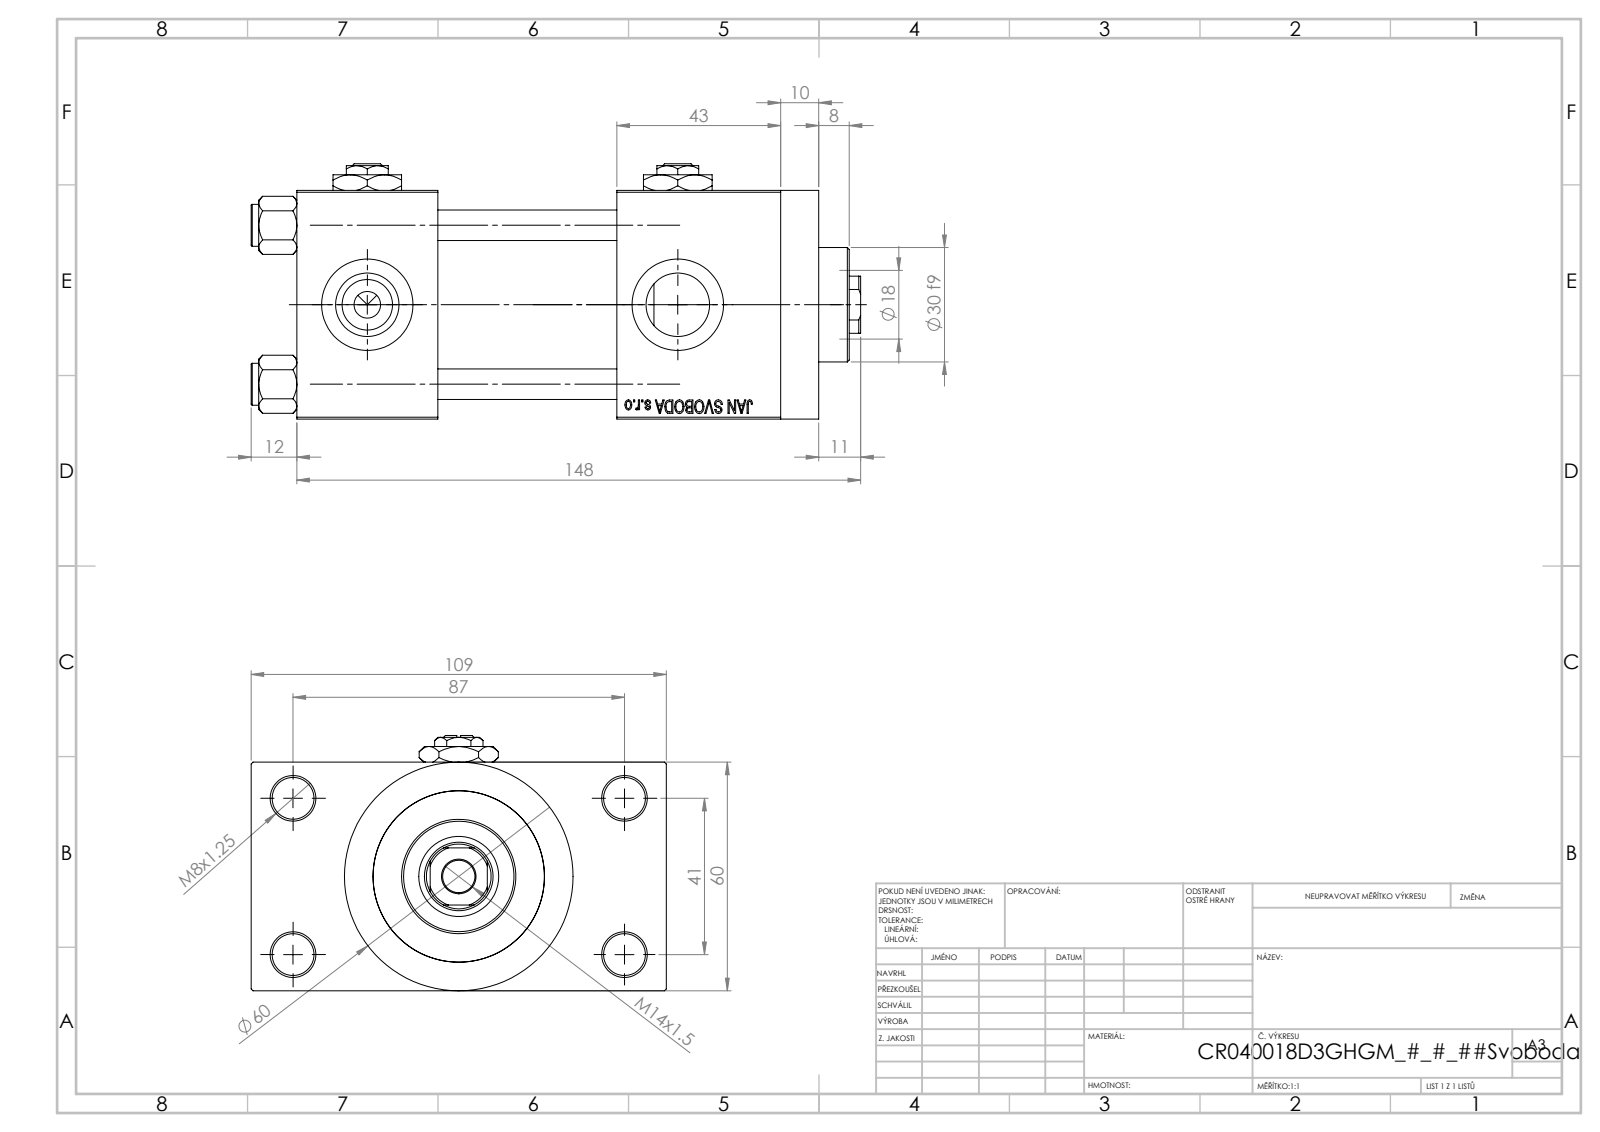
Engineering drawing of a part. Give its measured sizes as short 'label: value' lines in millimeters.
name: V215_VC_A; V215CR_D_TYCINKA; V215CR_VCP_D; V215CR_D_Body (+2 more)
written by: SolidWorks 2019 (CONFIG_CONTROL_DESIGN)
unit: mm
bodies: 13 solids, 1205 faces (546 planar, 99 cylindrical, 560 other)
size: 160 × 109 × 67
volume: 482 864 mm³; area: 117 231 mm²
holes: 4× ⌀8, 4× ⌀11, 4× ⌀16.66, 4× ⌀24, 3× ⌀7, 1× ⌀8.5, 1× ⌀18, 1× ⌀21, 1× ⌀31, 1× ⌀40, 1× ⌀45
bosses: 4× ⌀11, 1× ⌀60, 1× ⌀46, 1× ⌀30
rounds: 1× R8.5
face distances: 60, 47, 24.5, 84.5, 84, 37, 43, 127, 90, 10
hole spacings: 22.65, 29.49, 41.7, 47.15, 48.09, 64.35, 76.49, 41
